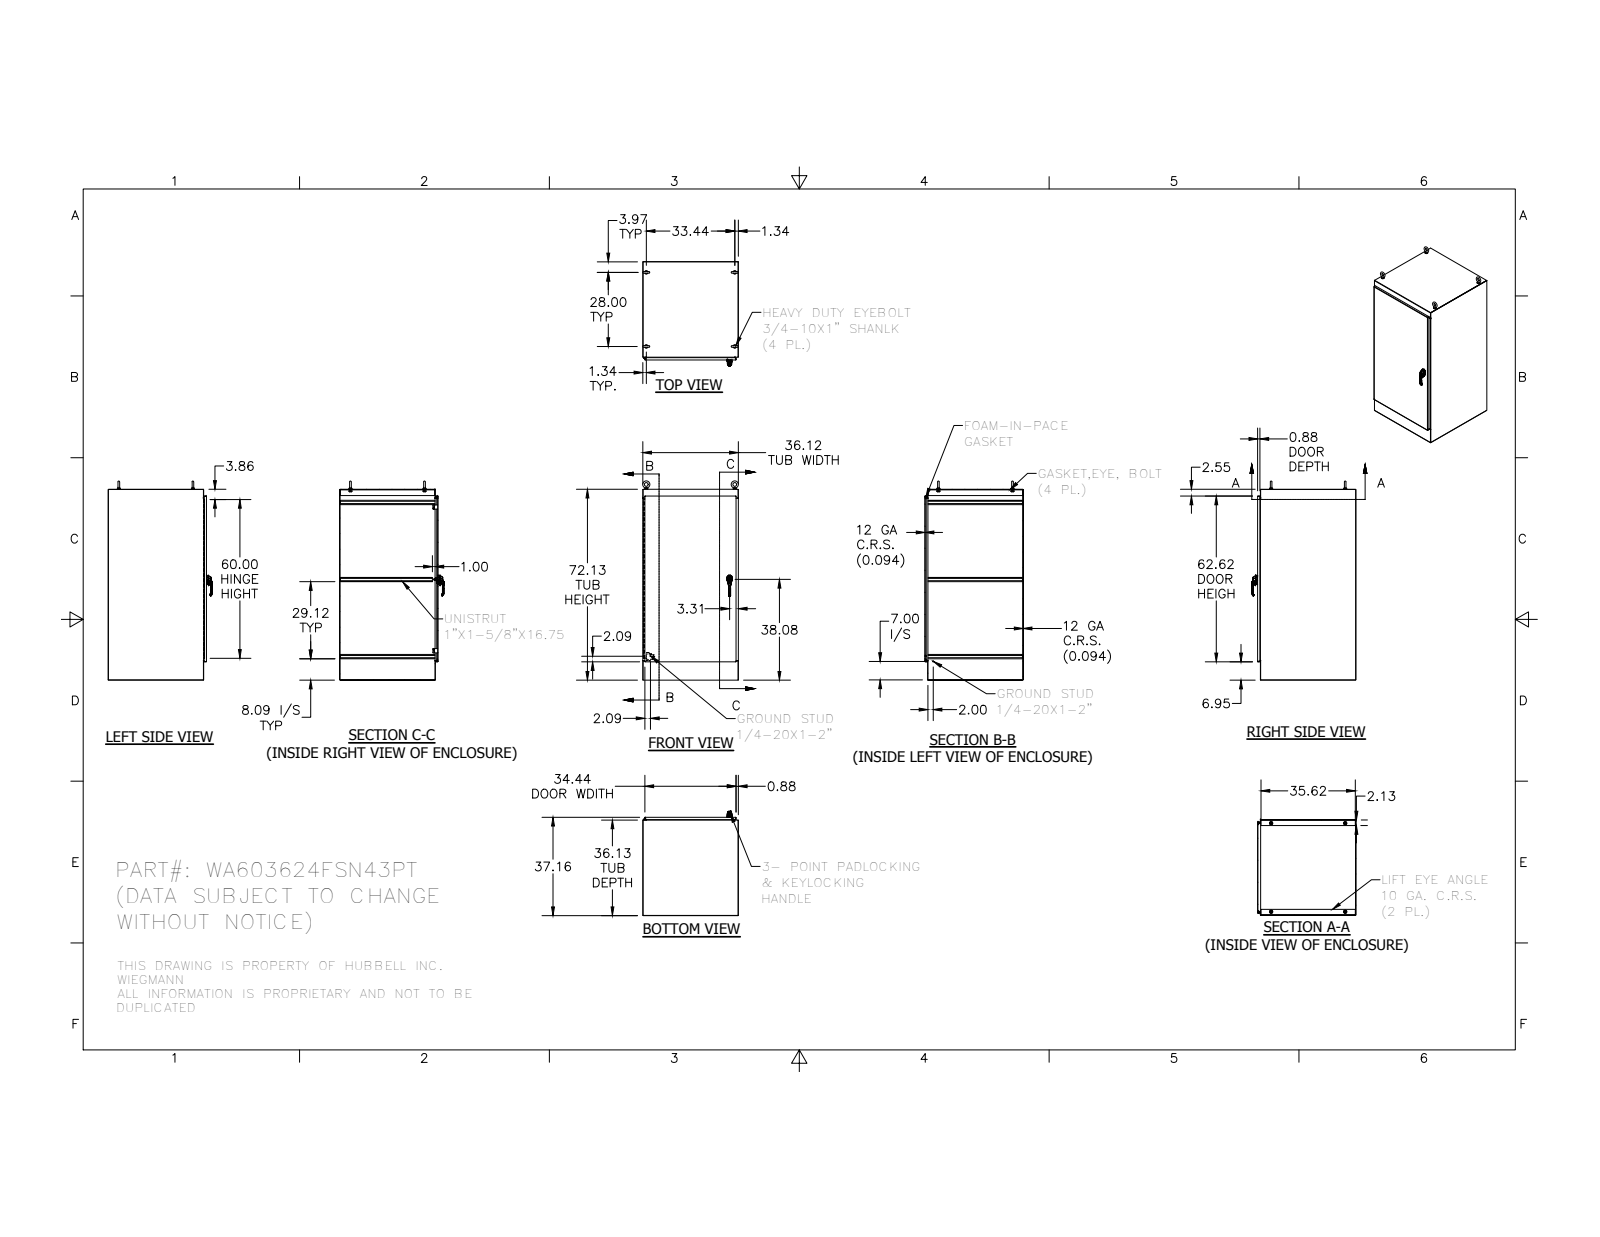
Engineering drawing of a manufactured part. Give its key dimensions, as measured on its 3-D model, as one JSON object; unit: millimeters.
{"part_name": "SUPPORT-ROLL_AF0; WA723636FSN43PT; 3065; HSSN1300W60 (+8 more)", "step_written_by": "SolidWorks 2014 (AUTOMOTIVE_DESIGN)", "units": "millimeters", "bodies": {"solids": 59, "faces": 2236, "planar": 862, "cylindrical": 844, "other": 530}, "overall_size": [1911.3, 943.9, 917.6], "volume_mm3": 24010000, "surface_area_mm2": 19570000, "round_holes": [[7, 8], [5.1, 4], [16.3, 4], [20.7, 4], [7.1, 3], [6.1, 2], [6.4, 2], [6.4, 2], [10.2, 2], [10.3, 2], [11.4, 2], [3.2, 1]], "round_bosses_or_shafts": [[31.8, 4], [28.4, 4], [19.1, 4], [6.4, 3], [25.4, 2], [14.3, 2], [13.4, 2], [12.7, 2]], "partial_cylinders_radius": [[0.3, 16], [0.8, 15], [1.3, 14], [3.2, 13], [0.5, 12], [1.3, 12], [2.2, 12], [3.2, 12]], "face_to_face_distances": [2.4, 915.2, 941.5, 912.8, 917.6, 1829.6, 939.1, 943.9, 1827.2, 1832], "hole_center_spacings": [1370.2, 1389.3, 19.4, 19.4, 30.4, 32.3, 711.2, 849.3]}
